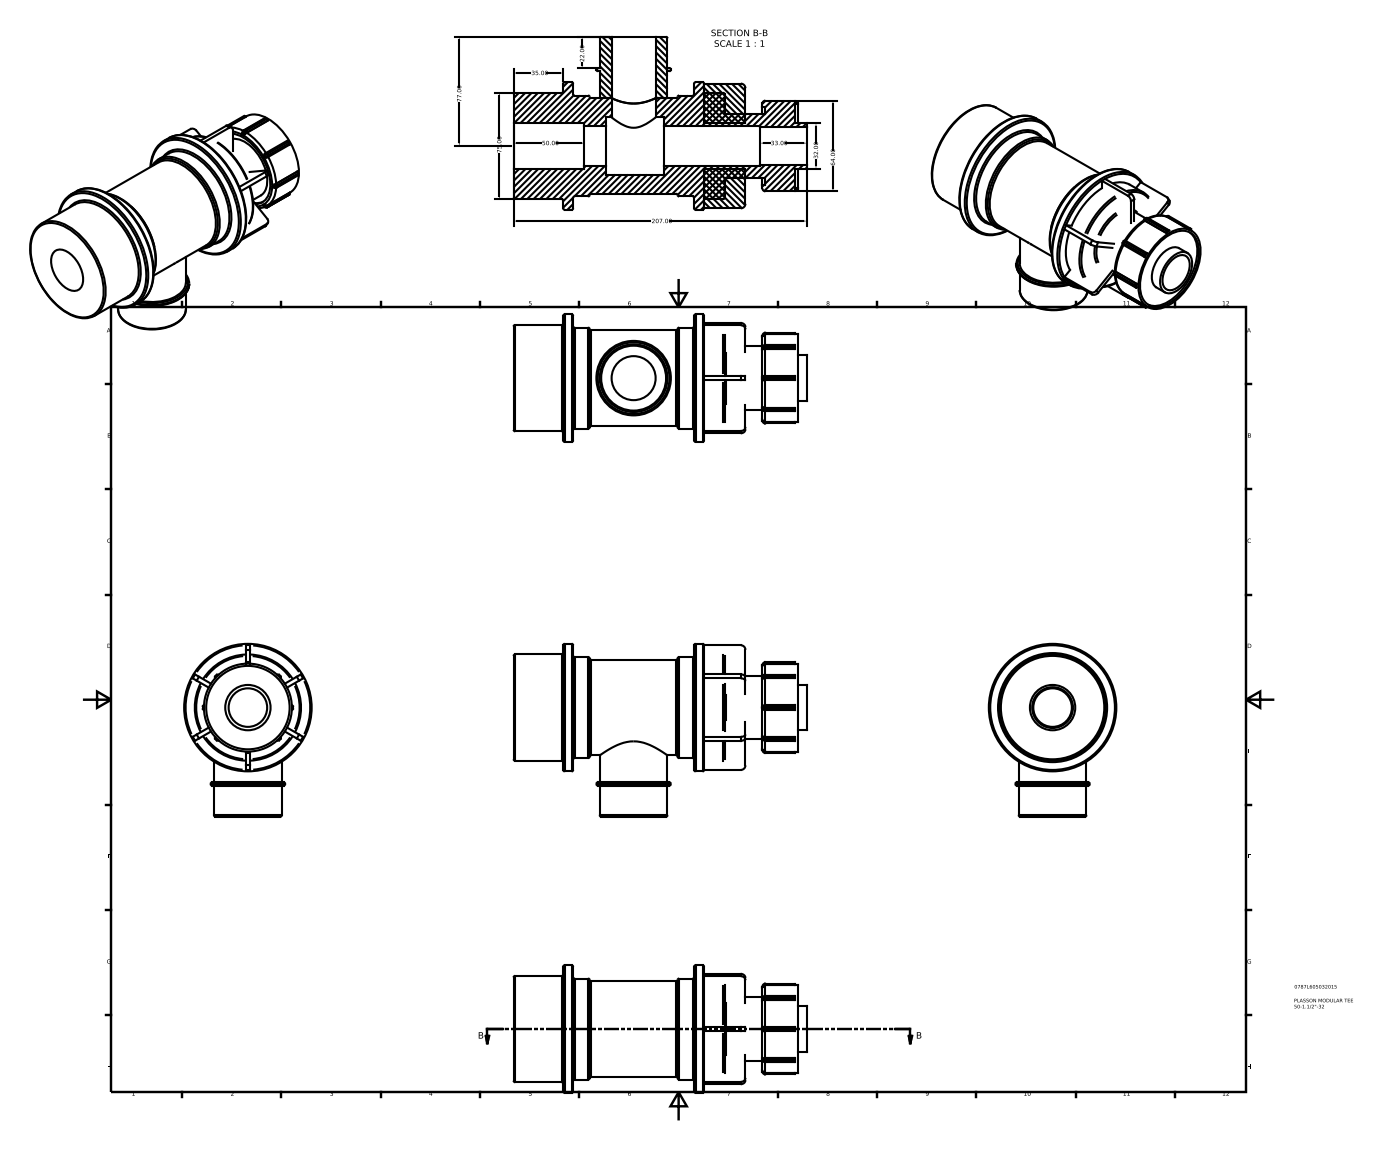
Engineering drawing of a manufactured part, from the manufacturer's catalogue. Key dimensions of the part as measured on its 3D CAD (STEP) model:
Part name (STEP PRODUCT): 0787L605032015
STEP written by: Autodesk Inventor 2015 (AUTOMOTIVE_DESIGN)
Units: millimetres
Bodies: 8 solids, 212 faces (86 planar, 69 cylindrical, 57 other)
Overall size (bounding box): 207 × 122 × 90
Volume: 629 181 mm³ · Surface area: 110 954 mm²
Round holes (diameter × count): ⌀27.2 ×1, ⌀28.8 ×1, ⌀31.07 ×1, ⌀32 ×1, ⌀40.32 ×1, ⌀54.4 ×1, ⌀58.88 ×1, ⌀67.5 ×1
Round bosses / shafts (diameter × count): ⌀90 ×1, ⌀75 ×1, ⌀71.25 ×1, ⌀62.08 ×1, ⌀52.58 ×1, ⌀47.8 ×1, ⌀45 ×1
Partial cylindrical surfaces — rounded edges, fillets, slot ends (radius × count): R1 ×28, R2 ×8, R3.2 ×6
Main face-to-face distances: 3.2, 92.4, 7, 148.92, 134.4, 14.52, 198.75, 64.35, 49.83, 42
